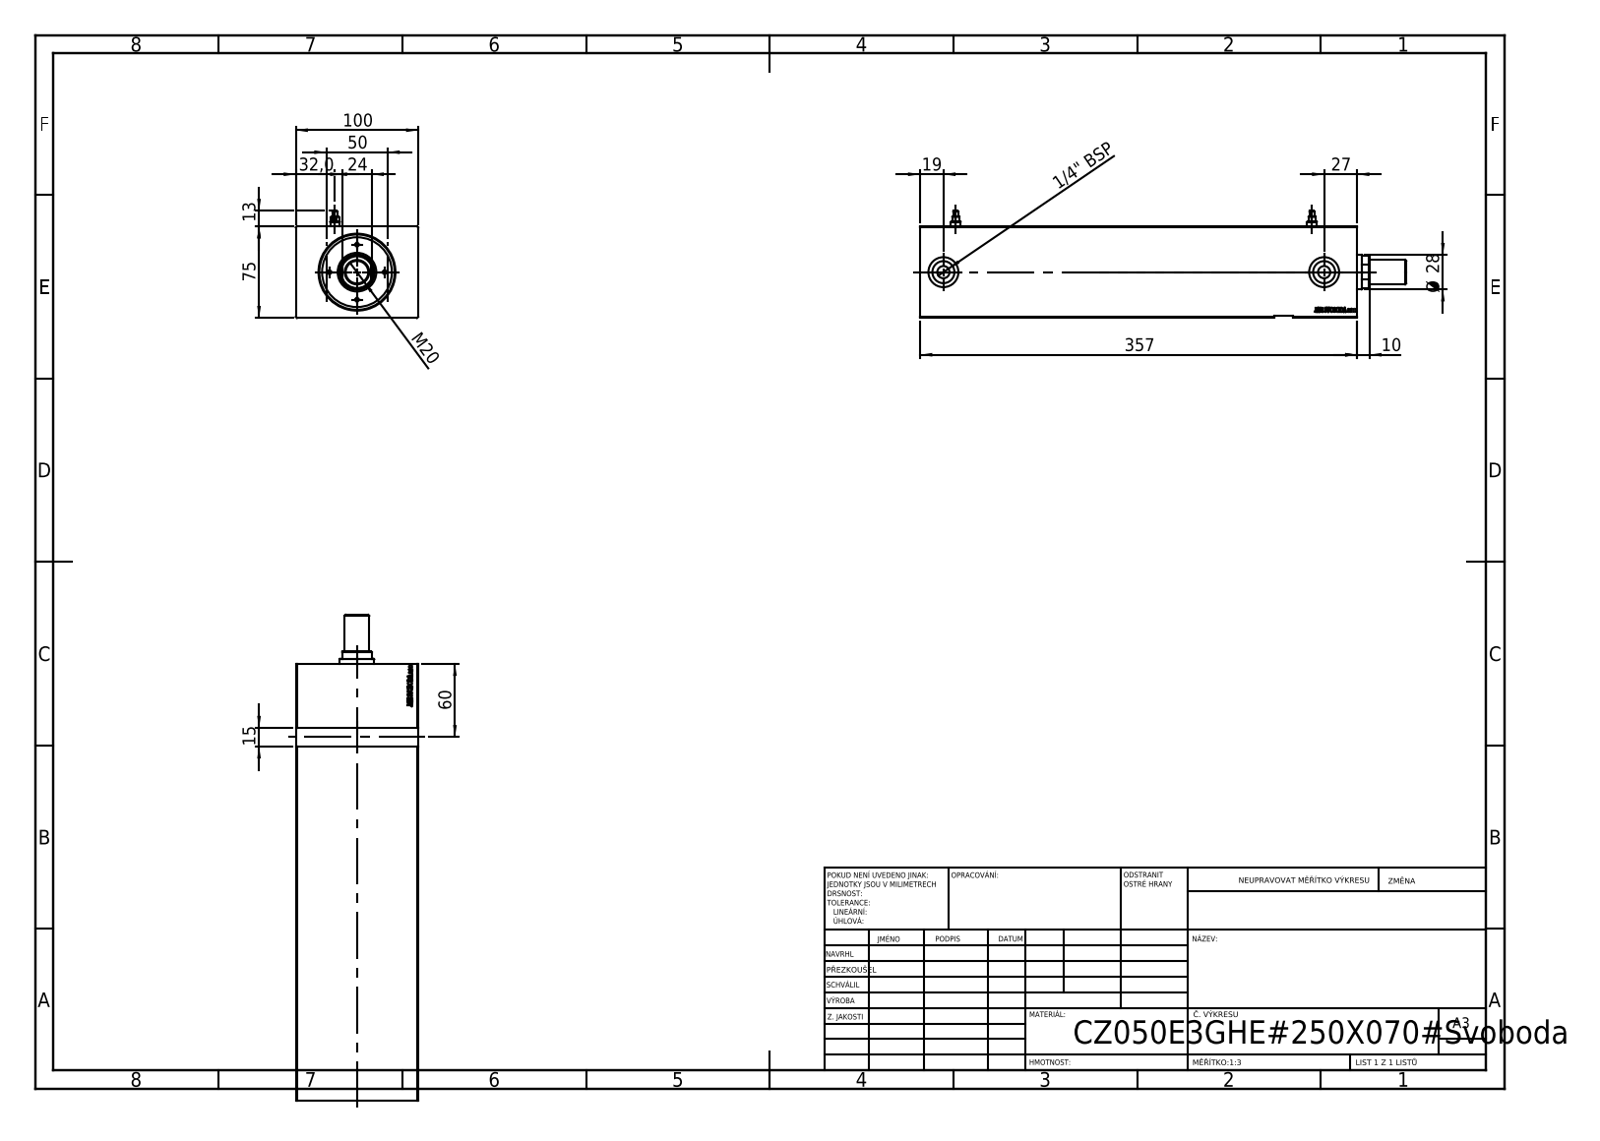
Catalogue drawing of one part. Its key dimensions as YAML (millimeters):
step_written_by: "SolidWorks 2019 (CONFIG_CONTROL_DESIGN)"
units: millimeters
bodies: {solids: 1, faces: 799, planar: 395, cylindrical: 22, other: 382}
overall_size: [357, 100, 75]
volume: 1989000
surface_area: 195263
round_holes:
  - {diameter: 8, count: 2}
  - {diameter: 10, count: 2}
  - {diameter: 18, count: 2}
  - {diameter: 24.5, count: 2}
  - {diameter: 36, count: 1}
  - {diameter: 50, count: 1}
  - {diameter: 61.5, count: 1}
face_to_face_distances: [75, 100, 357, 339.2, 17.8, 2, 73, 356.8, 17.6, 10]
hole_center_spacings: [291, 311]
